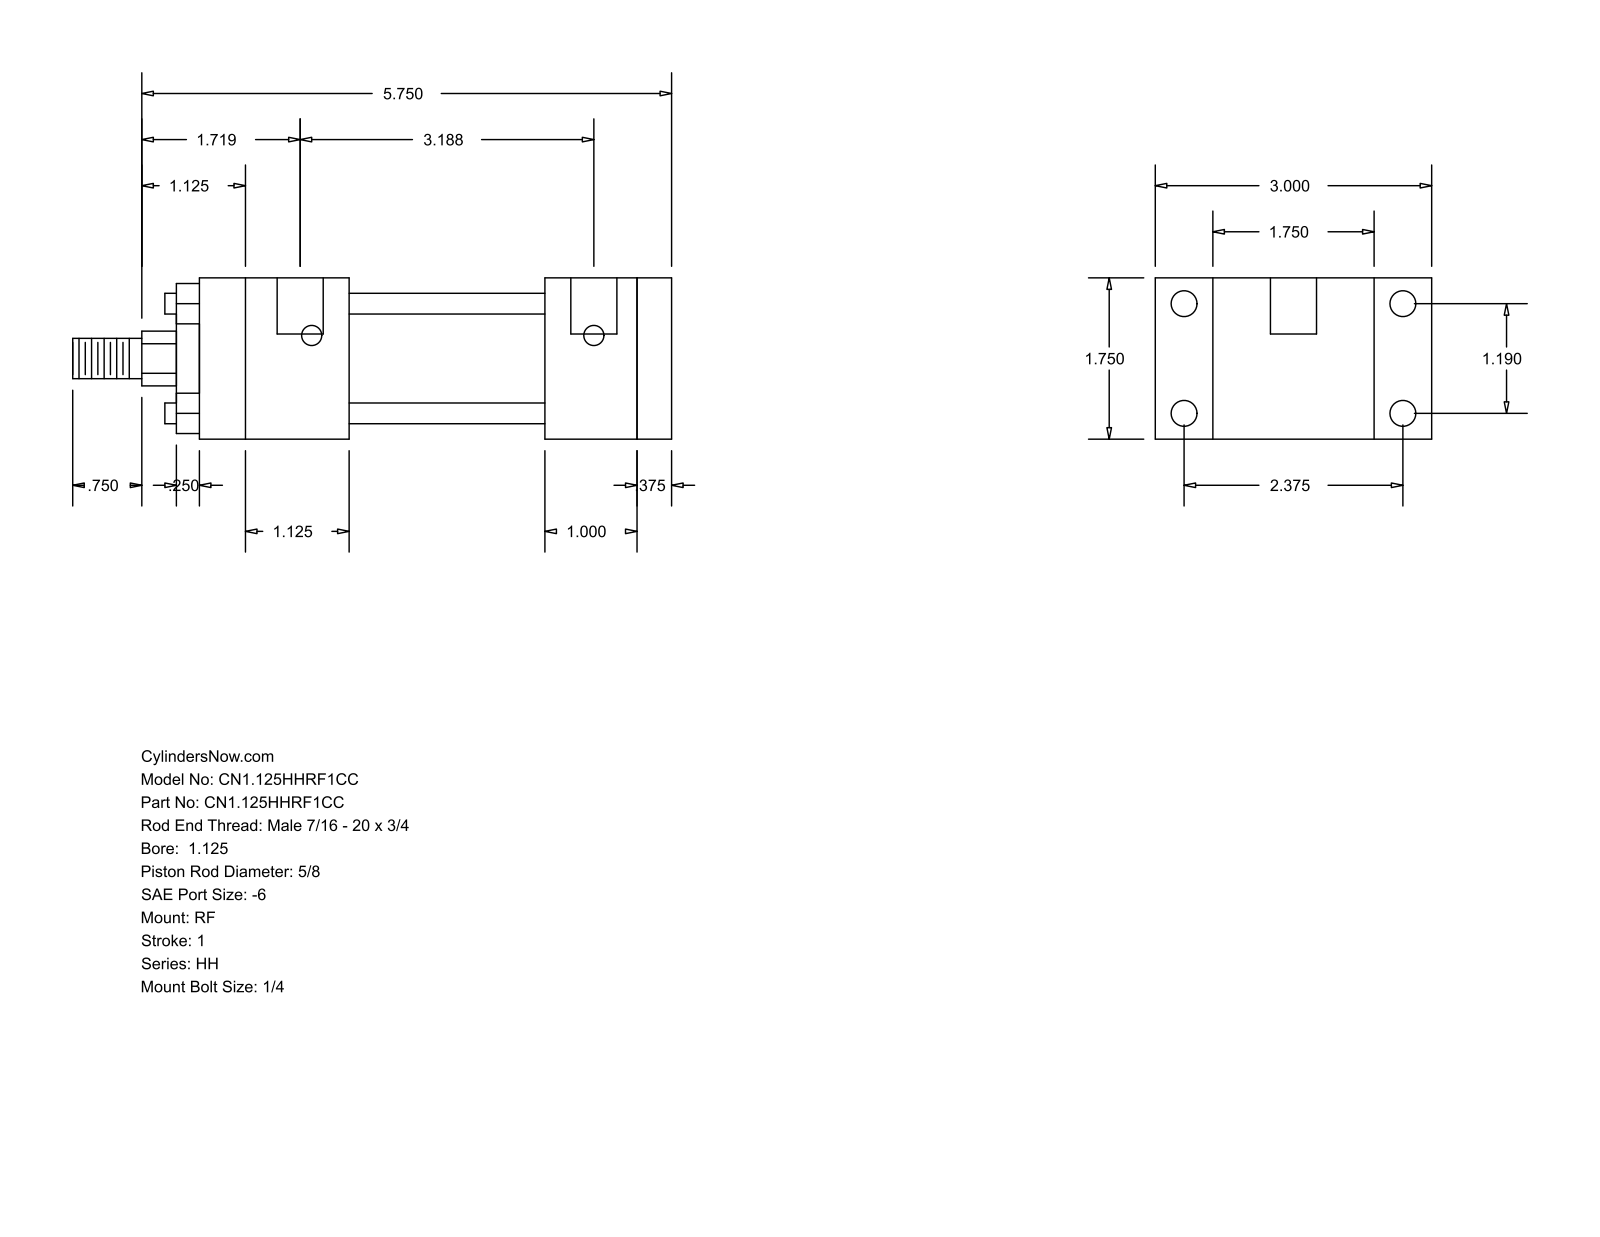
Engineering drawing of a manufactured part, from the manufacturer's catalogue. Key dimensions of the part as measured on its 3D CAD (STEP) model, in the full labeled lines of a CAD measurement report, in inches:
Part name (STEP PRODUCT): HH_RF__0112_0.625
STEP written by: GSSL Pune (CONFIG_CONTROL_DESIGN)
Units: inches
Bodies: 0 solids, 92 faces (64 planar, 28 cylindrical, 0 other)
Overall size (bounding box): 6.5 × 3 × 1.75
Round holes (diameter × count): ⌀0.219 ×4, ⌀0.281 ×4, ⌀0.5 ×2
Round bosses / shafts (diameter × count): ⌀0.225 ×4, ⌀1.375 ×1, ⌀1.125 ×1, ⌀0.625 ×1, ⌀0.437 ×1
Partial cylindrical surfaces — rounded edges, fillets, slot ends (radius × count): R0.297 ×1
Main face-to-face distances: 1.75, 0.375, 1.375, 5.125, 0.625, 3.125, 3.5, 2.125, 1, 1.625
Hole centre spacings: 1.19, 2.375, 2.656, 3.063, 0.125, 3.187
